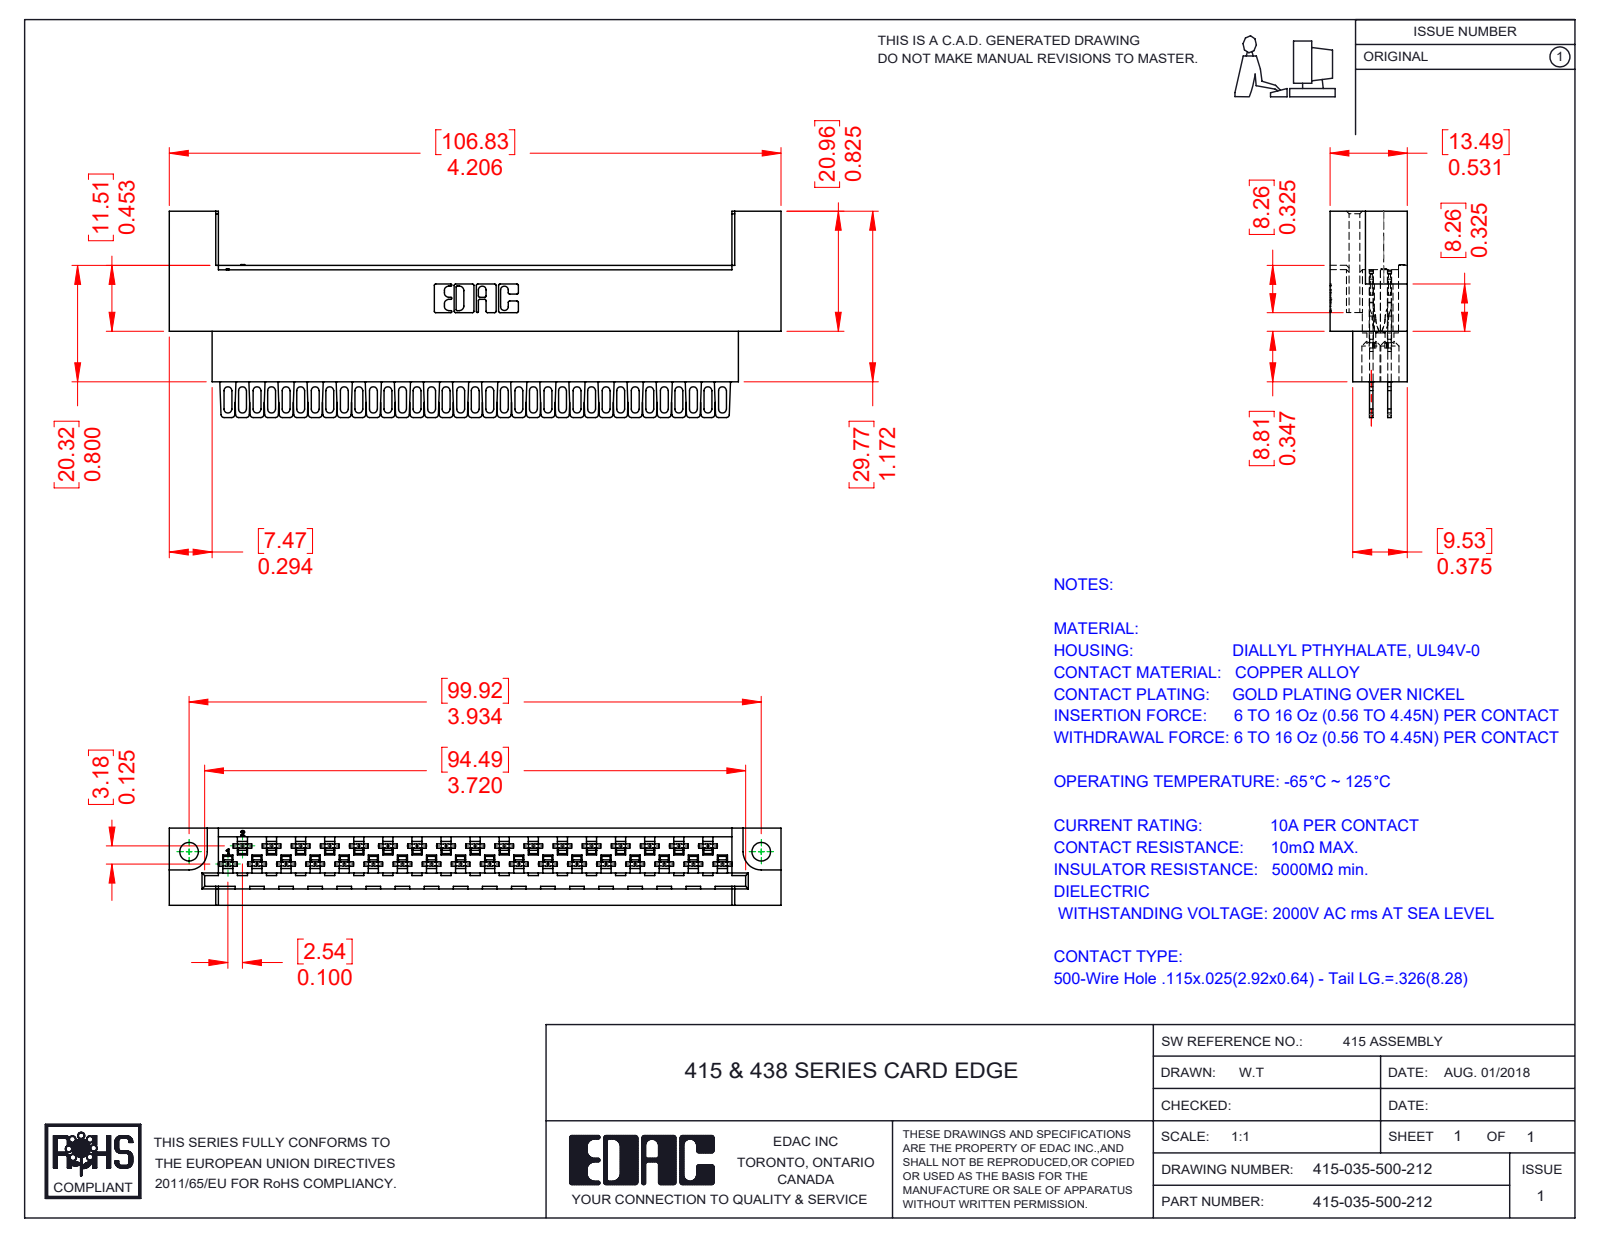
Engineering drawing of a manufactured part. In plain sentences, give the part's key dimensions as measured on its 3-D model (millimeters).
The part is named "516-290-001_500; 415-210-001_415-210-035-212; 415-035-500-212". Its 3-D file was written by "SolidWorks 2016 (CONFIG_CONTROL_DESIGN)". It is 36 solids with 3730 faces: 2332 planar, 1061 cylindrical and 337 other. Overall it measures 106.83 by 36 by 13.49 millimeters. Its volume is 19 043 cubic millimeters and its surface area 23 600 square millimeters. Round holes: 35 of diameter 1.27, 35 of diameter 3.3, 2 of diameter 3.25. Partial cylindrical surfaces (rounded edges, fillets, slot ends): 140 of radius 0.3, 140 of radius 0.56, 70 of radius 0.18, 70 of radius 0.2, 70 of radius 0.41, 70 of radius 0.51, 70 of radius 0.69, 70 of radius 2.03. The main face-to-face distances are 3.18, 0.61, 1.88, 13.49, 1.27, 7.49, 6.61, 6.88, 6, 2.82. The hole center spacings are 5.08, 10.16, 15.24, 20.32, 25.4, 30.48, 35.56, 2.54.
